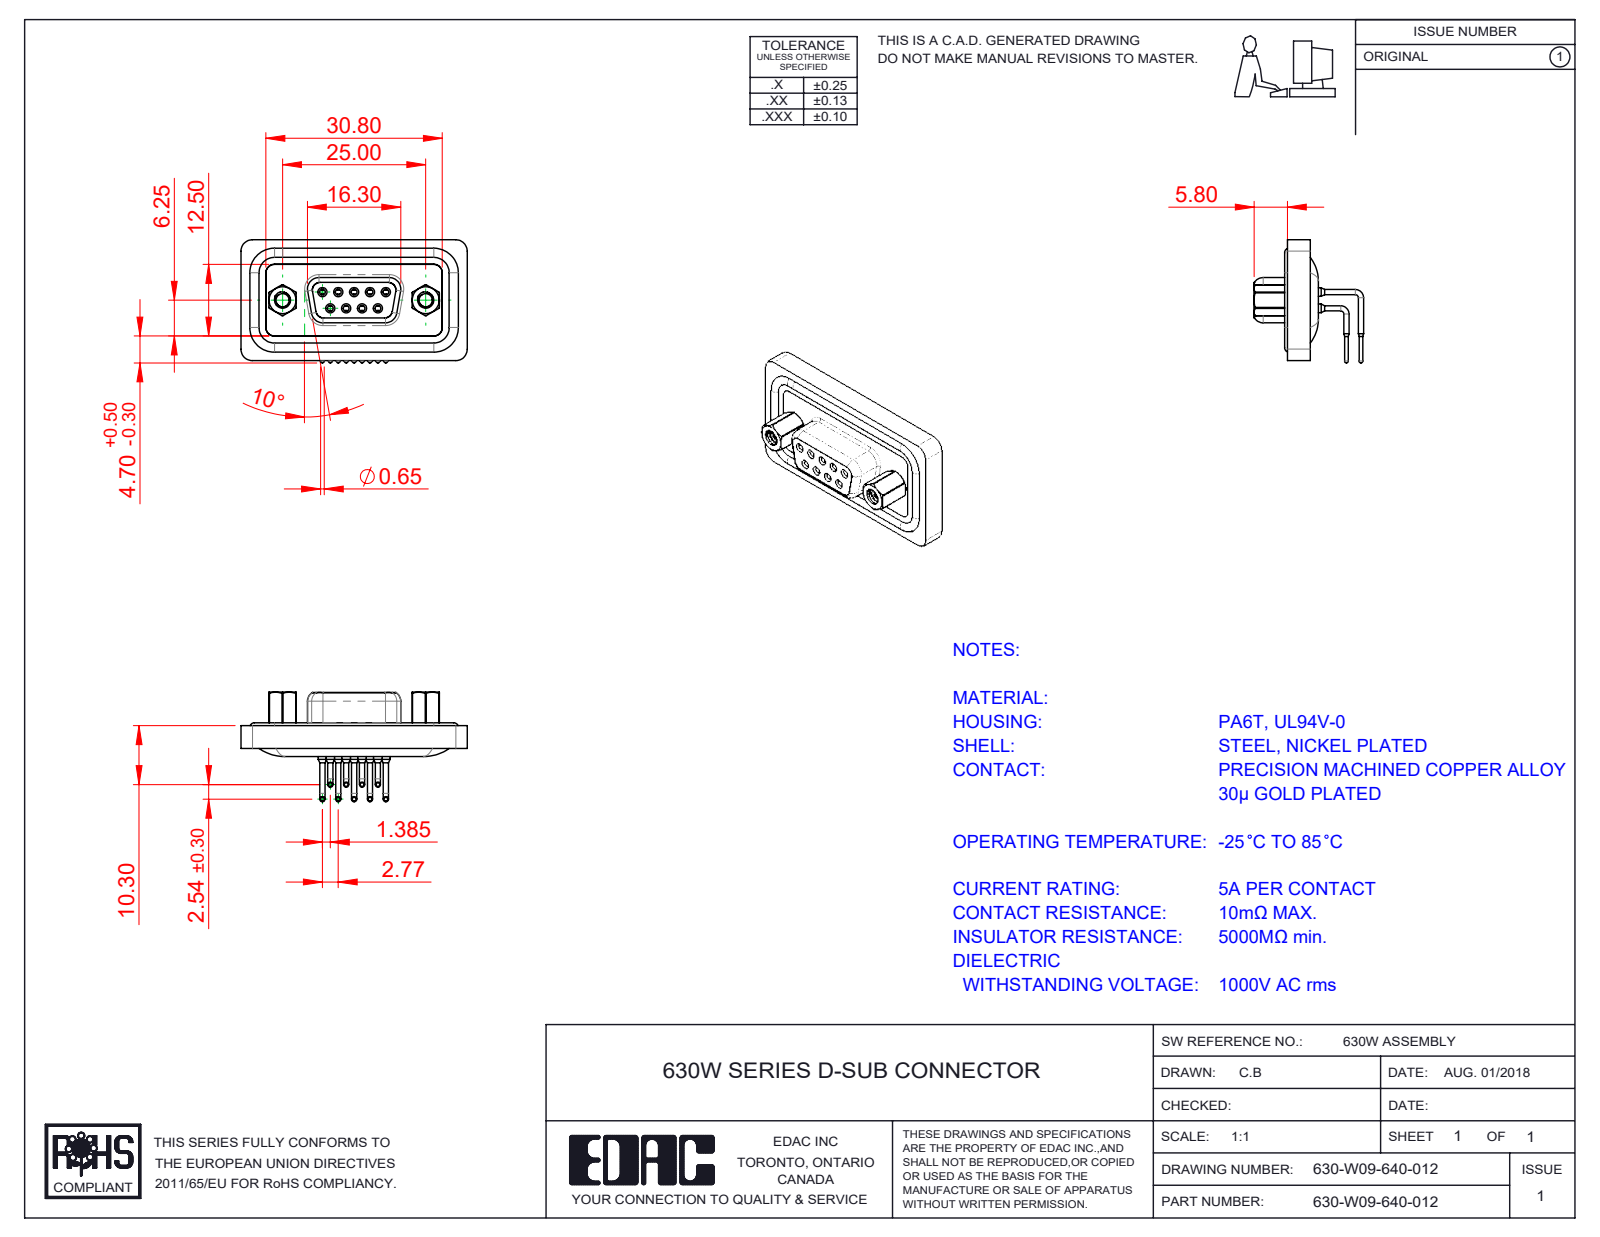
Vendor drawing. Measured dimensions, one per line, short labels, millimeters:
name: 630W 4-40 Threaded Rivet_Stabilizer; 630W 4-40 Hex Standoff; 630W Contact Row 1; 630W Shell_09 Contacts (+4 more)
written by: SolidWorks 2016 (CONFIG_CONTROL_DESIGN)
unit: mm
bodies: 17 solids, 910 faces (236 planar, 437 cylindrical, 237 other)
size: 39.51 × 21.5 × 19.14
volume: 4 411 mm³; area: 7 420 mm²
holes: 9× ⌀1, 9× ⌀1.1, 9× ⌀1.5, 9× ⌀1.7, 9× ⌀1.8, 9× ⌀2, 2× ⌀2.26, 2× ⌀2.29, 2× ⌀4, 2× ⌀4.8, 2× ⌀5
bosses: 18× ⌀0.9, 13× ⌀1.6, 9× ⌀0.65, 4× ⌀1.5, 2× ⌀4.9, 2× ⌀2.79, 1× ⌀5
rounds: 14× R1.5, 14× R2, 8× R1.35, 6× R2.7, 4× R0.5, 4× R0.9, 4× R1.6, 4× R1.75
face distances: 0.4, 1.6, 1.8, 1.1, 2.9, 2.5, 0.5, 3.6, 4, 0.7
hole spacings: 3.16, 2.77, 5.54, 5.03, 5.04, 7.48, 7.49, 8.31
